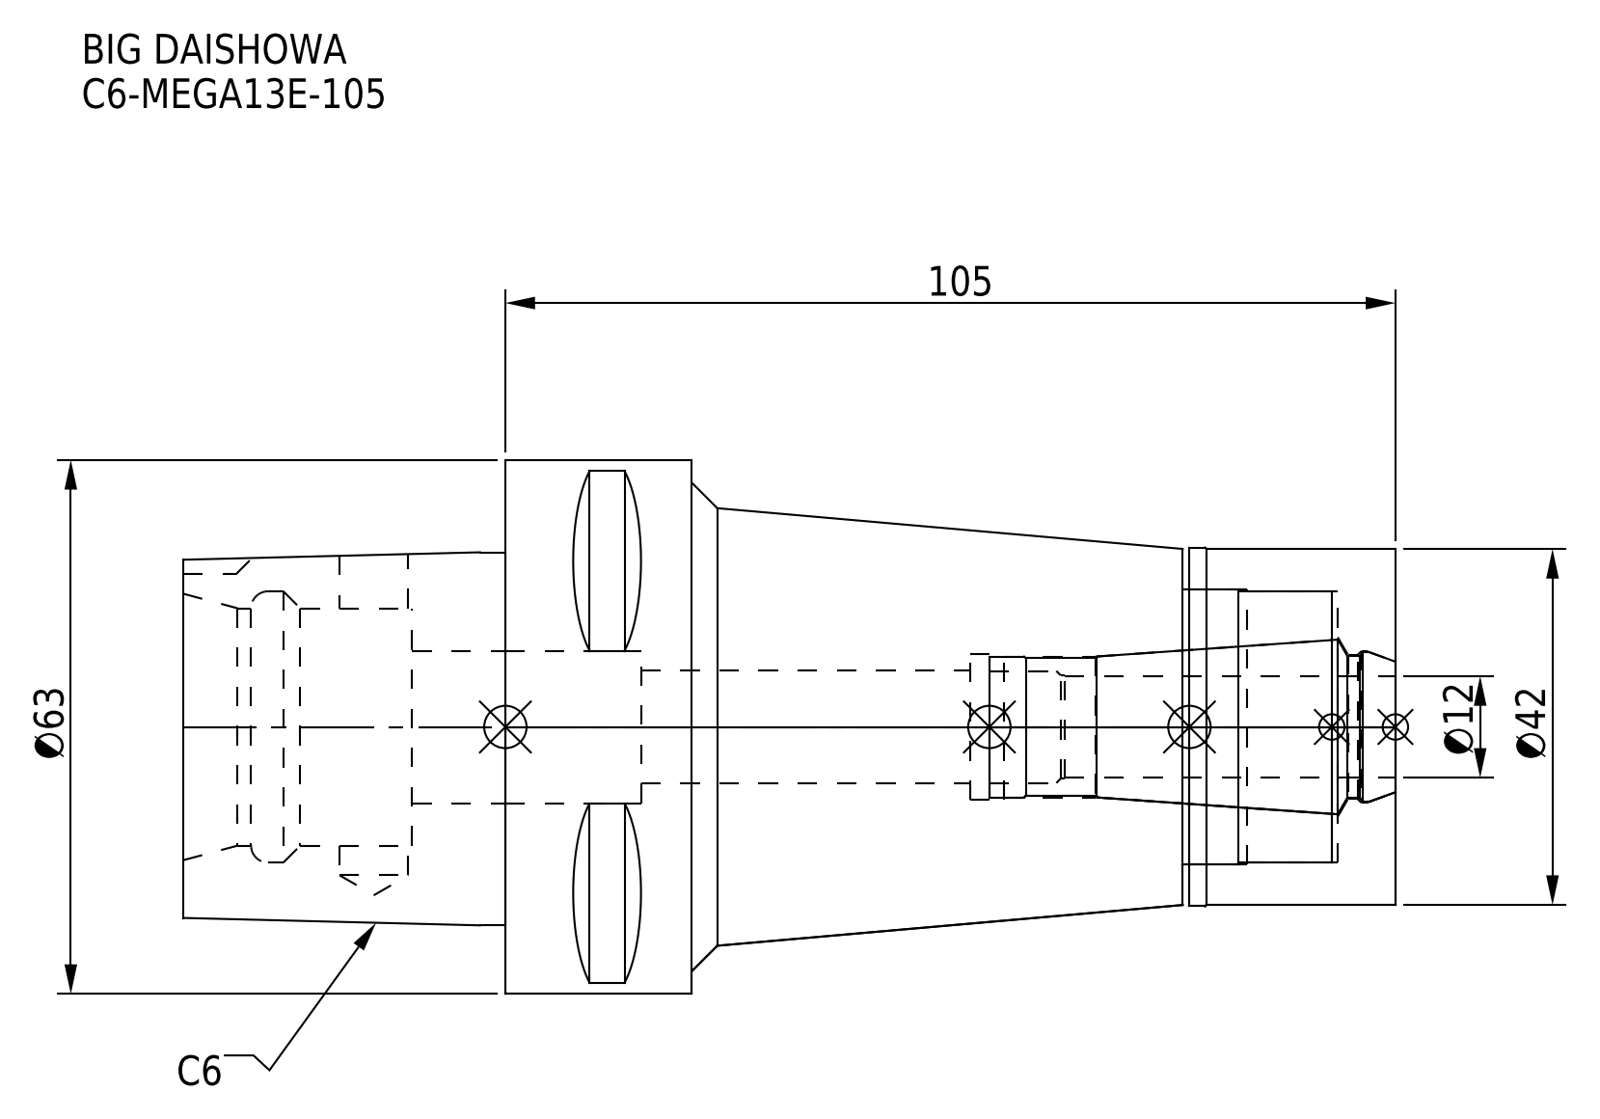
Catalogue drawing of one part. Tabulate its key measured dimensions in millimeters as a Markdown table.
| quantity | value |
| --- | --- |
| part name | DXF_TEMP_ASSY_ASM_4_ASM.stp; MEN13_1.stp; C6-MEGA13E-105-120-FreeParts; C6-MEGA13E-105-120.stp (+3 more) |
| STEP written by | SolidWorks 2019 (CONFIG_CONTROL_DESIGN) |
| units | millimeters |
| bodies | 2 solids, 97 faces (36 planar, 37 cylindrical, 24 other) |
| overall size | 143 × 63 × 63 |
| volume | 214 353 mm³ |
| surface area | 40 904 mm² |
| round holes (diameter × count) | 8.1 × 1, 13.3 × 1, 16.6 × 1, 17 × 1, 17.2 × 1, 17.9 × 1, 18 × 1, 28 × 1, 32 × 1, 32.5 × 1 |
| round bosses / shafts (diameter × count) | 63 × 1, 42.3 × 1, 42 × 1 |
| partial cylindrical surfaces (radius × count) | 5 × 1 |
| main face-to-face distances | 105, 25.1, 24.3, 80.7, 0.8, 79.9, 83, 58.7, 57.9, 22 |
